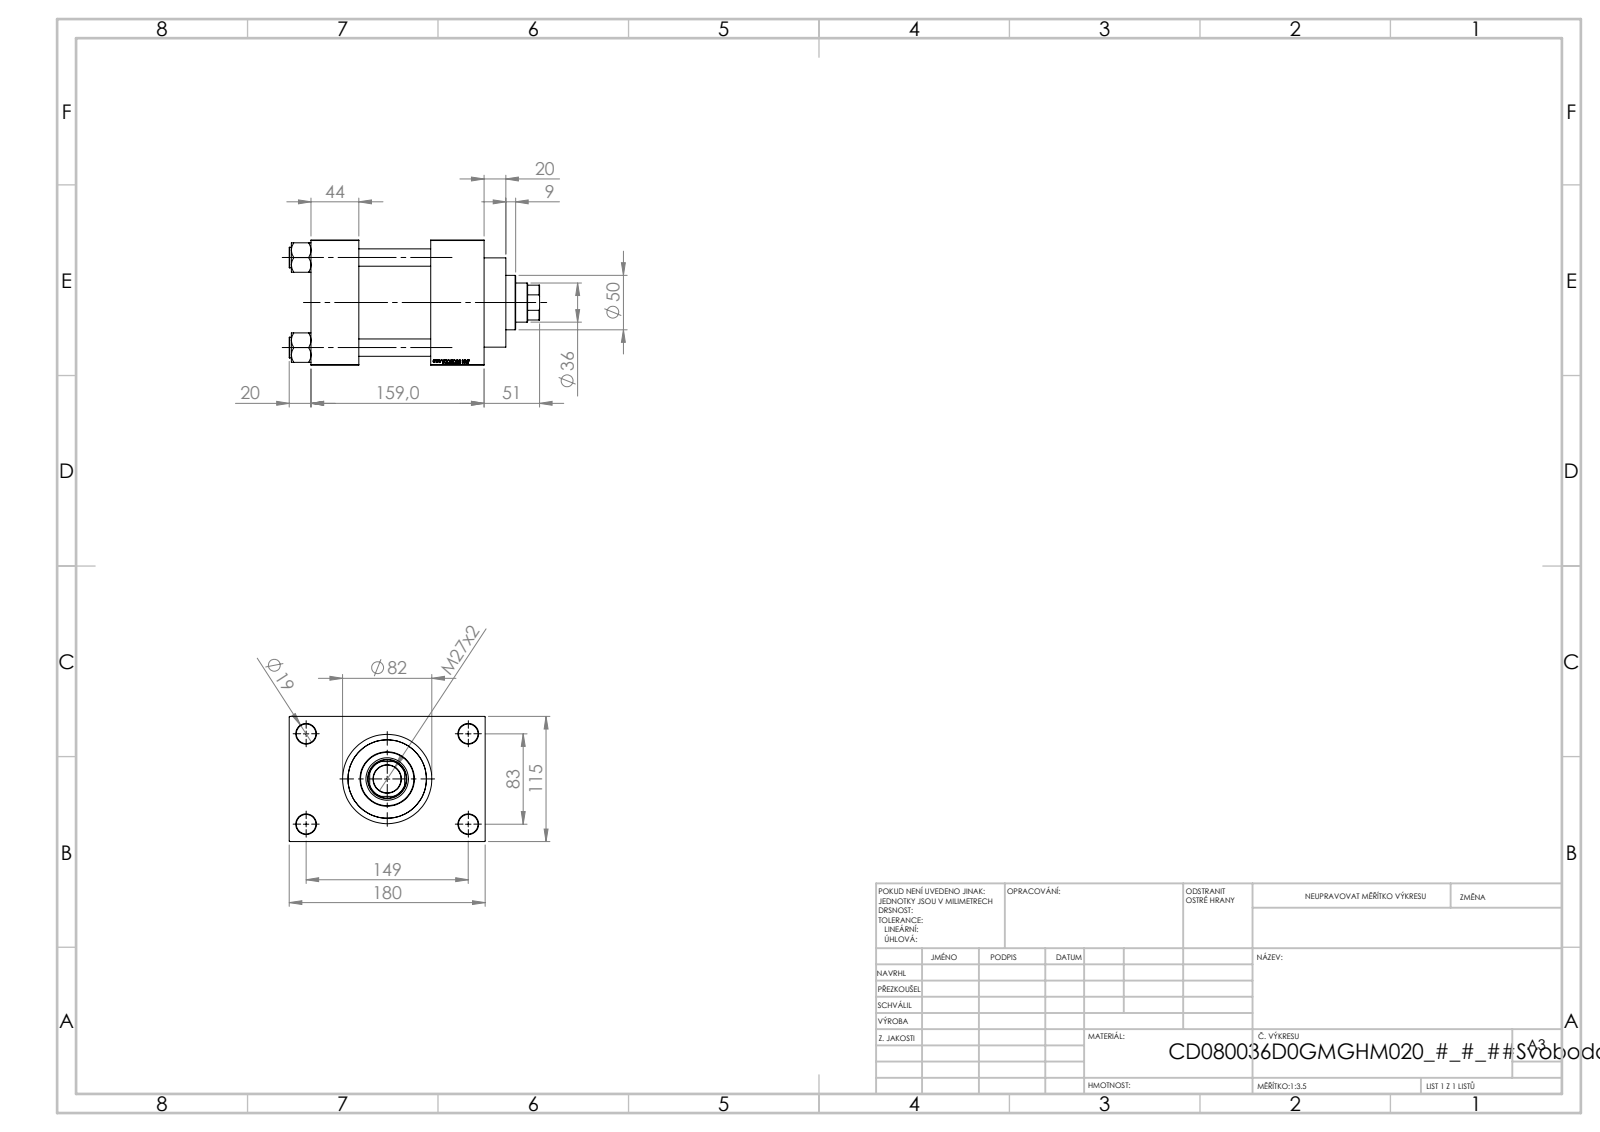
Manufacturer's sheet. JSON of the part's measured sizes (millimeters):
{"part_name": "V215CD_D_TYCINKA; V215CD_D_Body; V215CD_NUT_M5_D; V215CD_VC_A (+1 more)", "step_written_by": "SolidWorks 2019 (CONFIG_CONTROL_DESIGN)", "units": "millimeters", "bodies": {"solids": 11, "faces": 1151, "planar": 545, "cylindrical": 88, "other": 518}, "overall_size": [230, 180, 115], "volume_mm3": 1980000, "surface_area_mm2": 296453, "round_holes": [[16, 4], [18, 4], [7, 2], [26.44, 2], [35, 2], [25.5, 1], [36, 1], [39, 1], [61, 1], [72, 1], [80, 1]], "round_bosses_or_shafts": [[19, 4], [86, 1], [82, 1], [50, 1]], "partial_cylinders_radius": [[17.5, 1]], "face_to_face_distances": [115, 66, 110, 49, 44, 159, 32.5, 147.5, 20, 69], "hole_center_spacings": [33.15, 58.48, 82.7, 85.28, 89.24, 115.85, 142.43, 83]}
